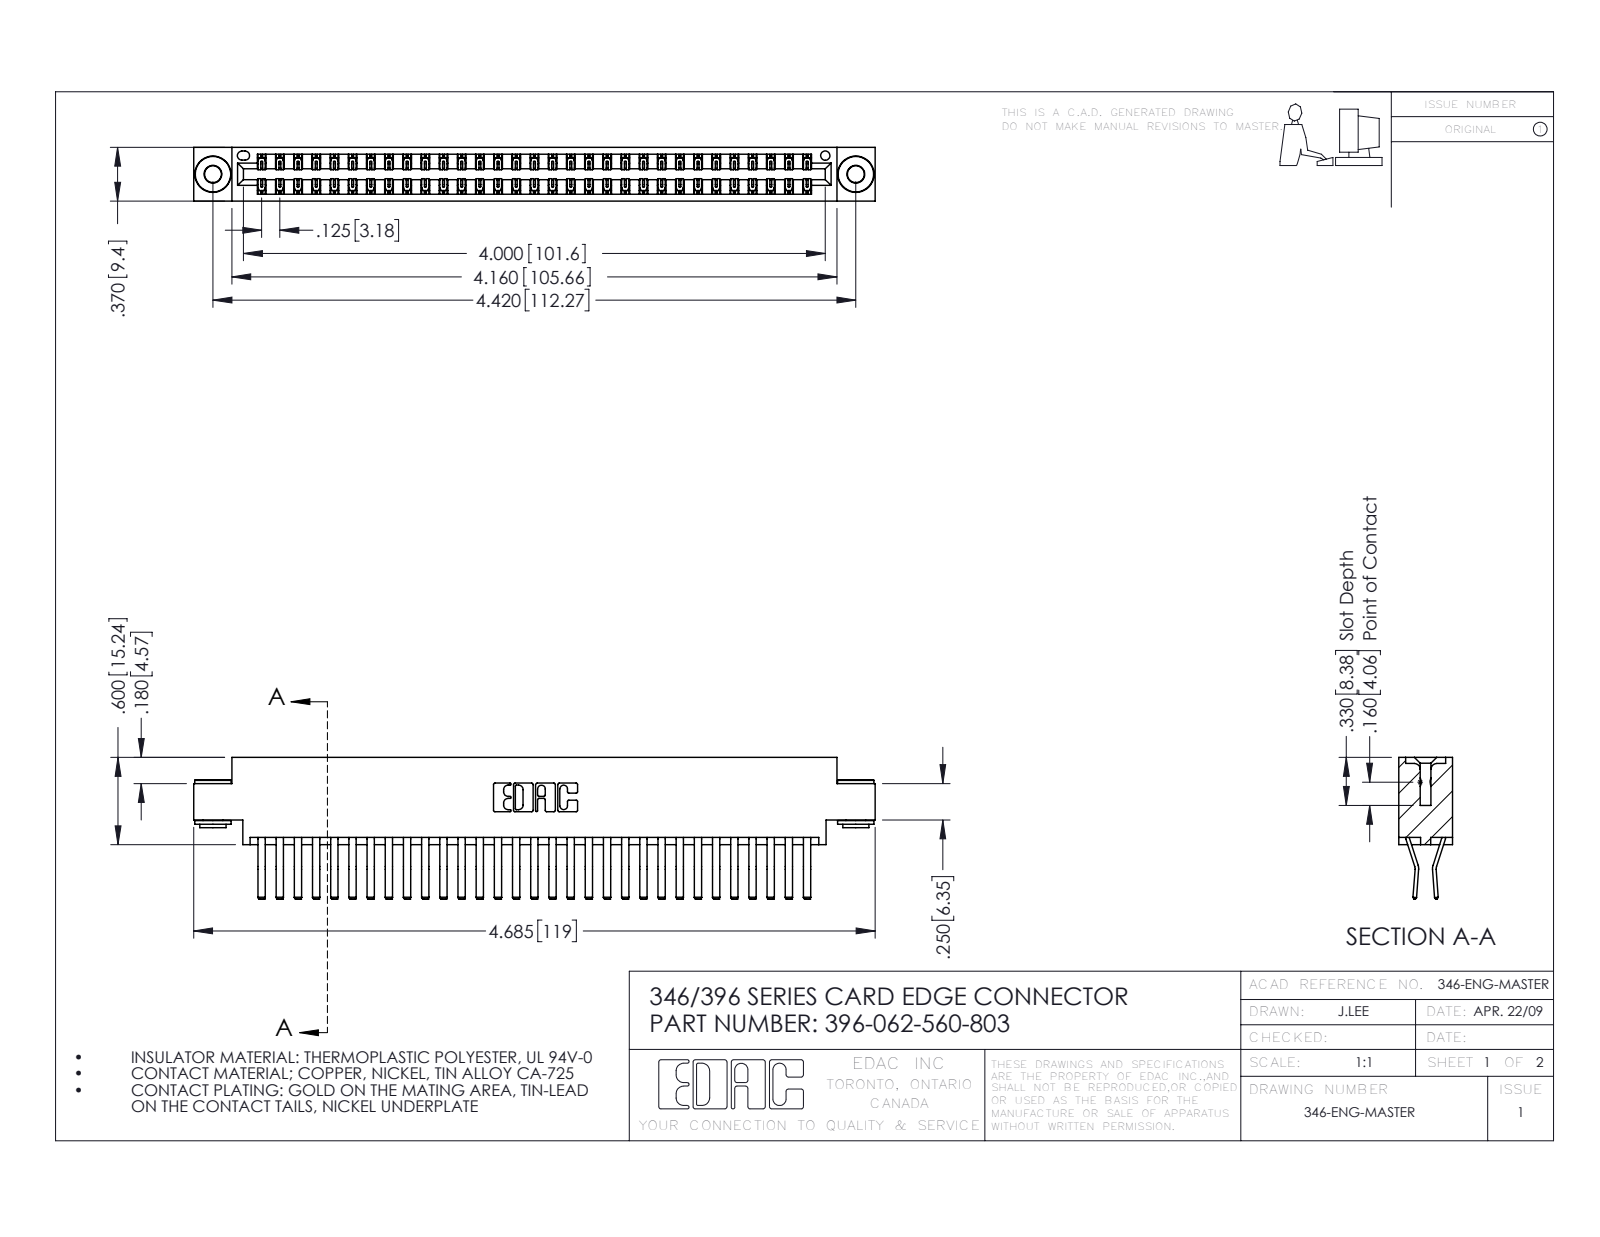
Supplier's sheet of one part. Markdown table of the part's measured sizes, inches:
| quantity | value |
| --- | --- |
| part name | 396-062-560-803; 346 Part_0.170 Offset - 0.156 Dia-TH; 345-250-002_345-250-002-102; 345-292-001_560 Tail |
| STEP written by | SolidWorks 2016 (CONFIG_CONTROL_DESIGN) |
| units | inches |
| bodies | 65 solids, 3512 faces (2260 planar, 1244 cylindrical, 8 other) |
| overall size | 4.685 × 0.975 × 0.37 |
| volume | 0.719 in³ |
| surface area | 27.14 in² |
| round holes (diameter × count) | 0.116 × 2, 0.156 × 2, 0.064 × 1 |
| round bosses / shafts (diameter × count) | 0.25 × 2, 0.18 × 2, 0.136 × 2 |
| partial cylindrical surfaces (radius × count) | 0.006 × 93, 0.01 × 22, 0.007 × 6, 0.031 × 6, 0.026 × 3, 0.01 × 2, 0.014 × 2, 0.022 × 2 |
| main face-to-face distances | 0.048, 0.322, 0.37, 0.025, 0.25, 0.275, 0.072, 0.298, 0.148, 0.222 |
| hole center spacings | 0.246, 4.212, 4.42 |
